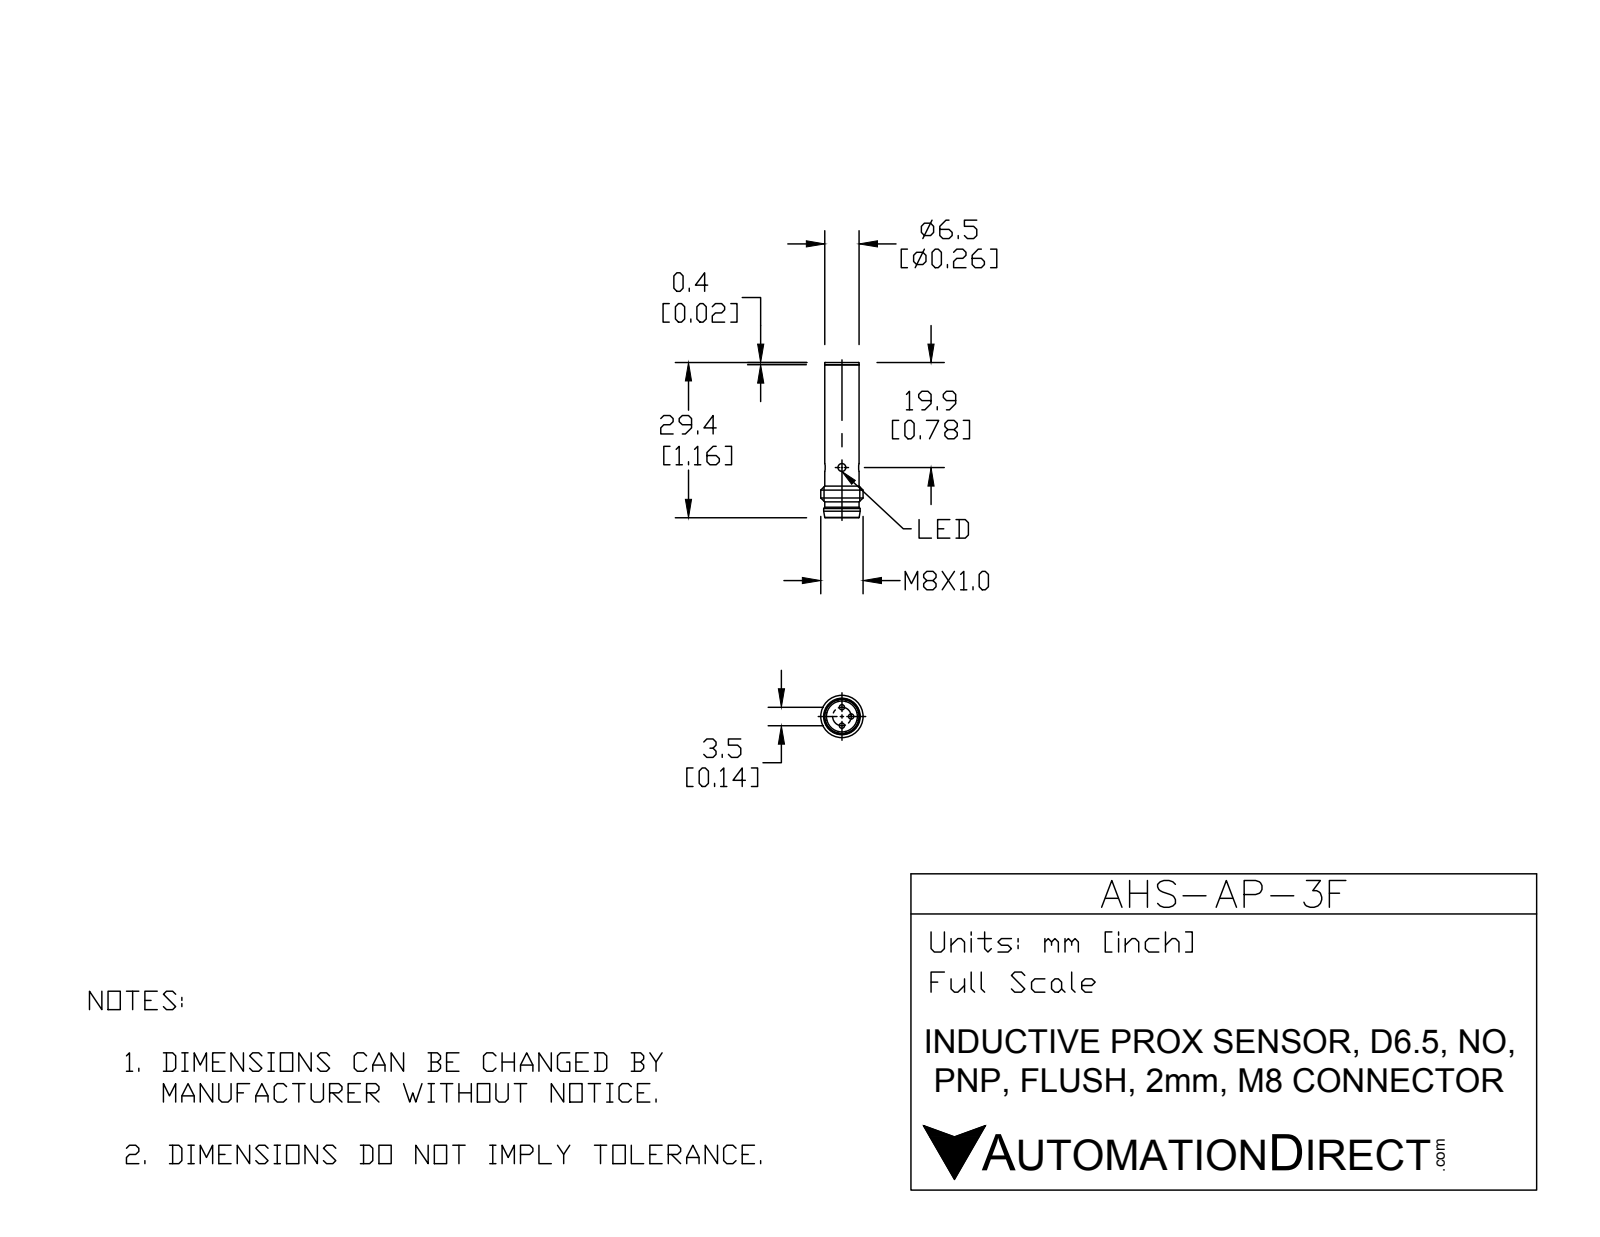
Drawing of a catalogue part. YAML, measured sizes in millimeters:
part_name: "AHS-AP-3F"
step_written_by: "SolidWorks 2015 (CONFIG_CONTROL_DESIGN)"
units: millimeters
bodies: {solids: 4, faces: 56, planar: 12, cylindrical: 26, other: 18}
overall_size: [29.4, 8, 8]
volume: 891
surface_area: 842
round_holes:
  - {diameter: 1.5, count: 2}
  - {diameter: 5.85, count: 1}
round_bosses_or_shafts:
  - {diameter: 1, count: 3}
  - {diameter: 8, count: 1}
  - {diameter: 6.9, count: 1}
  - {diameter: 6.5, count: 1}
face_to_face_distances: [24.4, 3, 27.4, 5.5, 2, 5, 29.4, 29, 27, 24]
